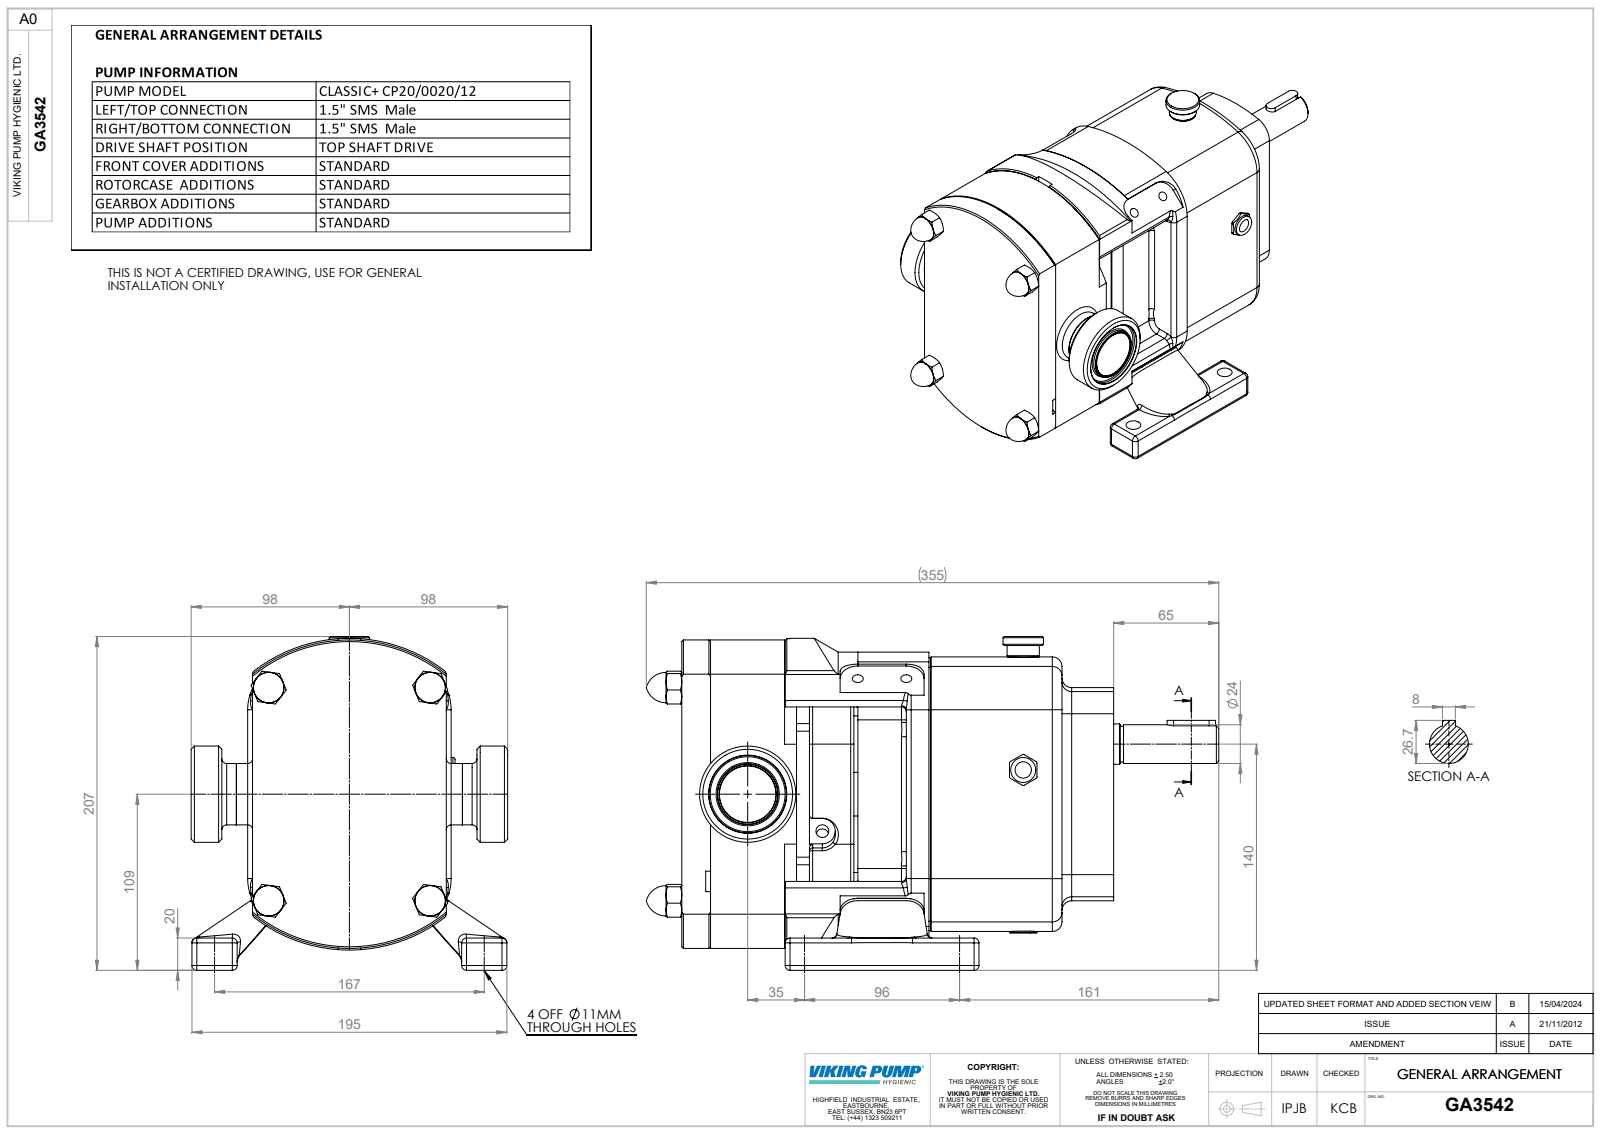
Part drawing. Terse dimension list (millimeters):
name: Copy of Z94-5101-22 - 1.5 INCH SMS681^GA3542; GA3542; CP20-0020-12 H T
written by: SolidWorks 2023 (AUTOMOTIVE_DESIGN)
unit: mm
bodies: 3 solids, 847 faces (257 planar, 292 cylindrical, 298 other)
size: 354.54 × 206.69 × 196
volume: 4 809 000 mm³; area: 304 102 mm²
holes: 4× ⌀6.8, 4× ⌀11, 3× ⌀6.47, 2× ⌀8, 1× ⌀22.53, 1× ⌀35, 1× ⌀48
bosses: 2× ⌀35, 2× ⌀17, 1× ⌀59.6, 1× ⌀38, 1× ⌀37.6, 1× ⌀25.02, 1× ⌀25, 1× ⌀24
rounds: 55× R3, 18× R2, 16× R1, 8× R6, 8× R11.1, 6× R1.27, 6× R4, 6× R8
face distances: 120, 109.04, 158.4, 267.44, 25, 95, 20.27, 99.73, 4.73, 74.73
hole spacings: 53.7, 30.05, 92.35, 96, 167.02, 61.08, 159.1, 159.11
